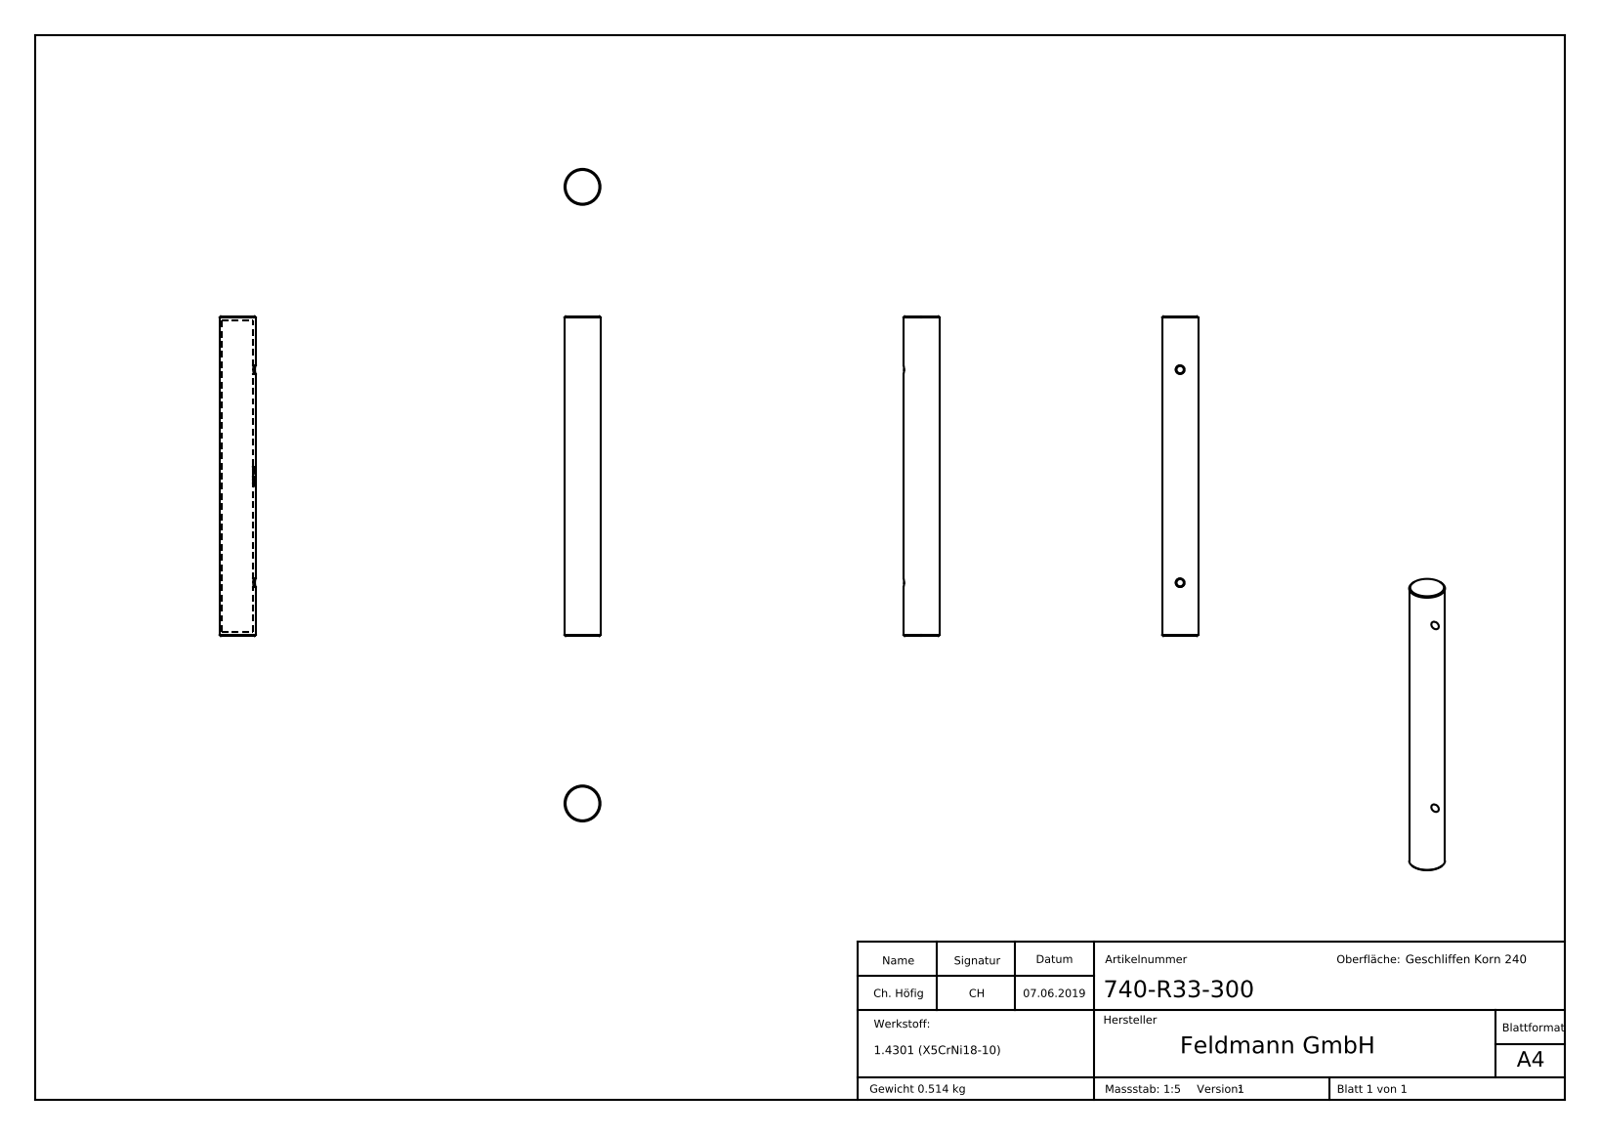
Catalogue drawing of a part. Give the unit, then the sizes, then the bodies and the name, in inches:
Units: inches
Overall size (bounding box): 11.811 × 1.327 × 1.327
Round holes (diameter × count): ⌀0.268 ×2, ⌀1.169 ×1
Round bosses / shafts (diameter × count): ⌀1.327 ×1
Partial cylindrical surfaces — rounded edges, fillets, slot ends (radius × count): R0.589 ×1
Main face-to-face distances: 0.157, 11.654, 11.811, 11.496, 0.435, 0.08, 0.084, 0.431, 0.023, 0.515
Hole centre spacings: 7.874
Volume: 3.968 in³ · Surface area: 96.07 in²
Bodies: 1 solid, 270 faces (105 planar, 35 cylindrical, 130 other)
Part name (STEP PRODUCT): 740-R33-300
STEP written by: SolidWorks 2015 (CONFIG_CONTROL_DESIGN)
